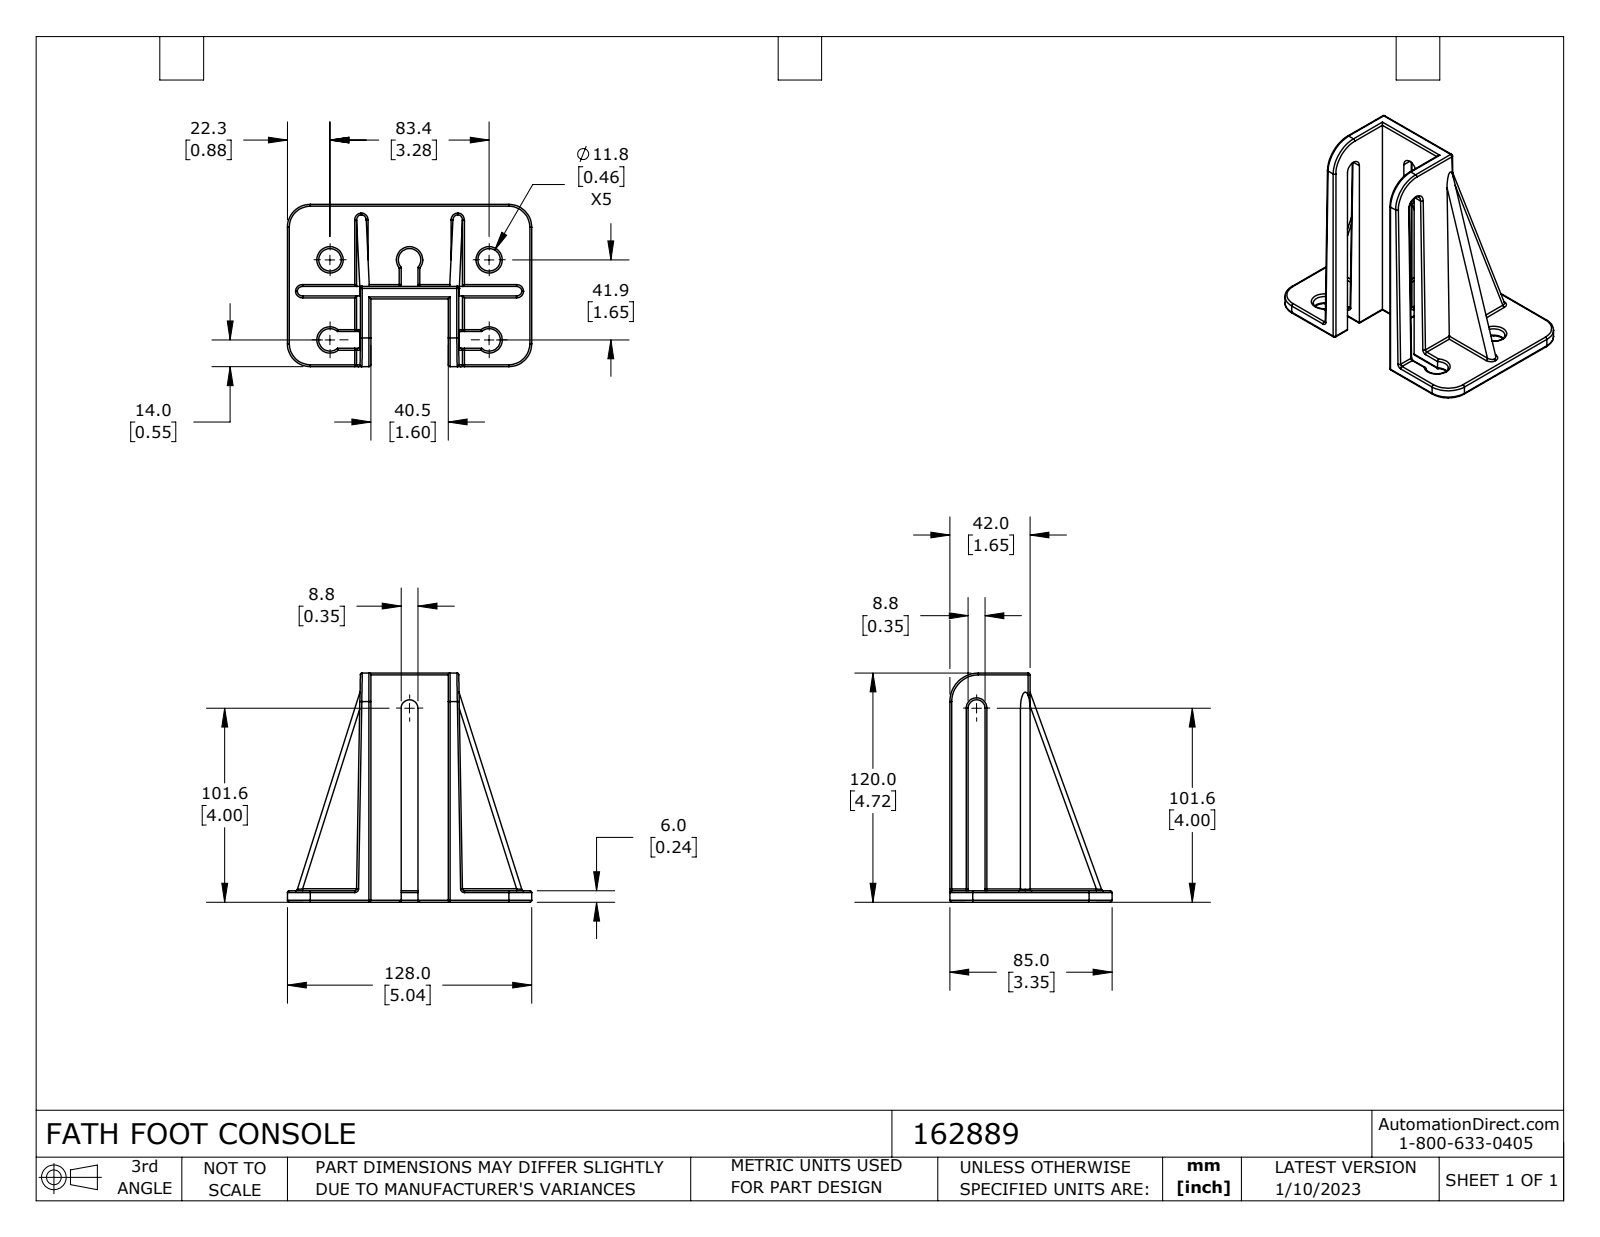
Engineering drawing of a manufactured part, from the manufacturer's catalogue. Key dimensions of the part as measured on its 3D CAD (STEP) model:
Part name (STEP PRODUCT): 162889
STEP written by: SolidWorks 2021 (CONFIG_CONTROL_DESIGN)
Units: inches
Bodies: 1 solid, 172 faces (28 planar, 85 cylindrical, 59 other)
Overall size (bounding box): 5.039 × 4.724 × 3.346
Volume: 9.693 in³ · Surface area: 94.54 in²
Round holes (diameter × count): ⌀0.465 ×2
Partial cylindrical surfaces — rounded edges, fillets, slot ends (radius × count): R0.039 ×43, R0.098 ×4, R0.472 ×4, R0.232 ×3, R0.173 ×2, R0.591 ×1
Main face-to-face distances: 0.236, 0.197, 0.256, 1.595, 0.059, 0.346, 1.02, 1.079, 1.276, 0.673
Hole centre spacings: 3.282
